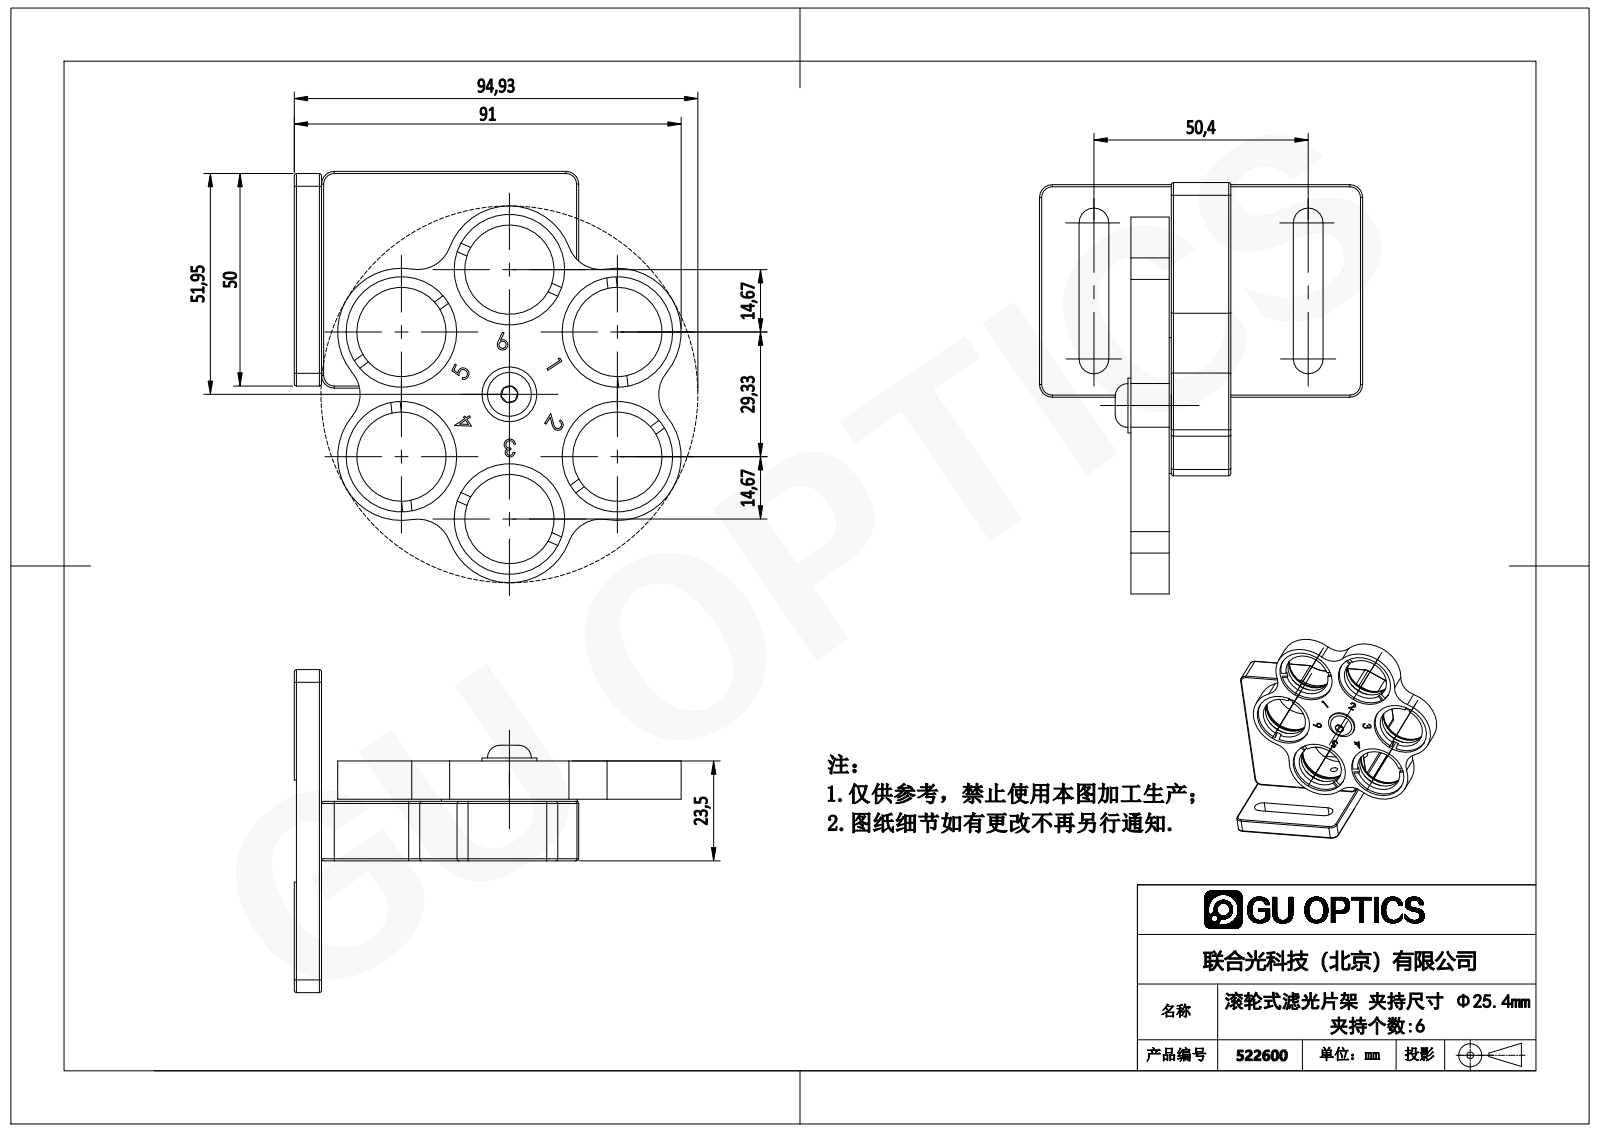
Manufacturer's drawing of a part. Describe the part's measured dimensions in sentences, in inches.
The part is named "M-FW1-6". Its 3-D file was written by "SolidWorks 2012 (CONFIG_CONTROL_DESIGN)". It is 0 solids with 247 faces: 131 planar, 90 cylindrical and 26 other. Overall it measures 3.81 by 3.583 by 2.992 inches. Round holes: 7 of diameter 0.906, 6 of diameter 0.827, 6 of diameter 0.866, 6 of diameter 1.024, 2 of diameter 0.13, 2 of diameter 0.157, 2 of diameter 0.295. Round bosses or shafts: 2 of diameter 0.26, 1 of diameter 1.26, 1 of diameter 0.508. Partial cylindrical surfaces (rounded edges, fillets, slot ends): 22 of radius 0.02, 11 of radius 0.118, 6 of radius 0.315, 6 of radius 0.591, 4 of radius 0.138. The main face-to-face distances are 0.02, 0.252, 0.551, 0.354, 0.374, 0.925, 0.571, 0.118, 0.047, 0.319. The hole center spacings are 1.155, 2, 2.309, 0.984, 2, 1.154, 2.309.
